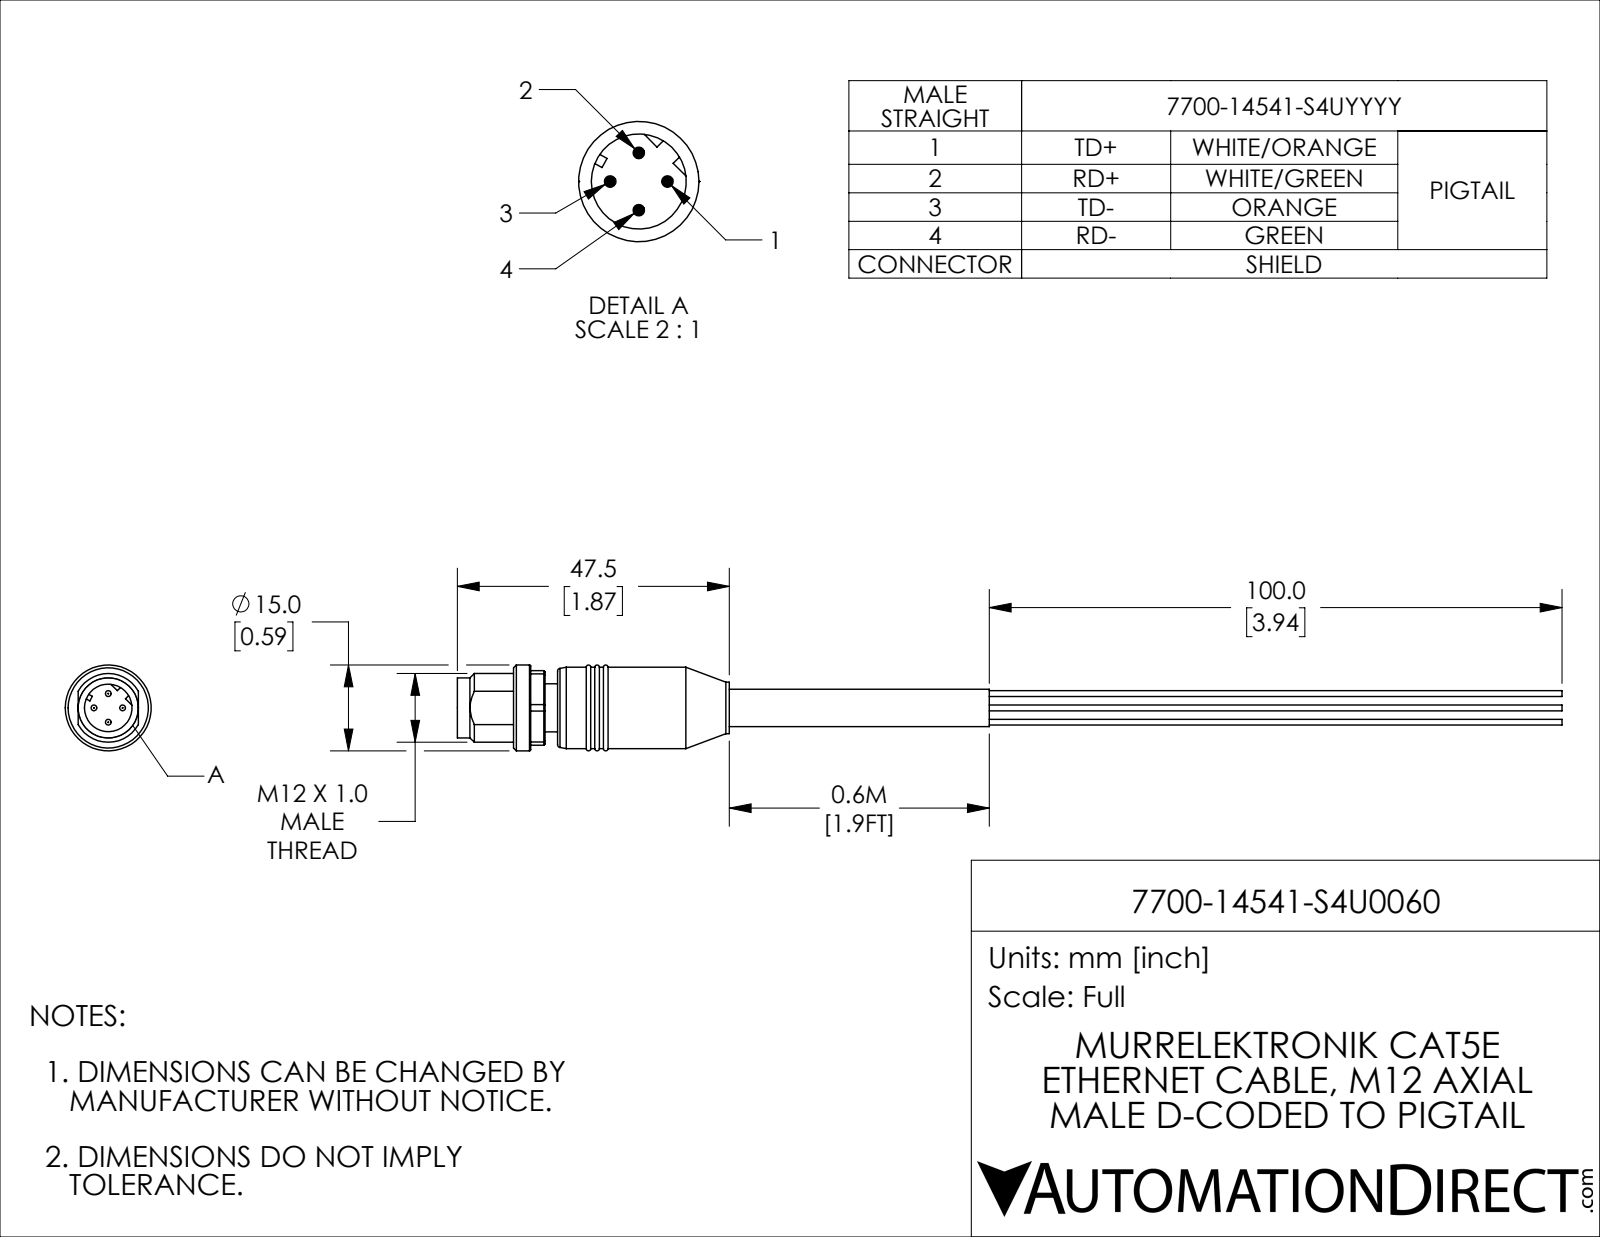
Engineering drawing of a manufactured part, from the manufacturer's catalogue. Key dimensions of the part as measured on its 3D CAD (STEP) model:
Part name (STEP PRODUCT): 7700-14541-S4U0060
STEP written by: SolidWorks 2021 (CONFIG_CONTROL_DESIGN)
Units: inches
Bodies: 1 solid, 125 faces (40 planar, 45 cylindrical, 40 other)
Overall size (bounding box): 7.594 × 0.591 × 0.591
Volume: 0.473 in³ · Surface area: 7.675 in²
Round holes (diameter × count): ⌀0.327 ×1
Round bosses / shafts (diameter × count): ⌀0.039 ×4, ⌀0.591 ×1, ⌀0.559 ×1, ⌀0.413 ×1, ⌀0.354 ×1, ⌀0.331 ×1, ⌀0.256 ×1
Partial cylindrical surfaces — rounded edges, fillets, slot ends (radius × count): R0.236 ×1, R0.283 ×1
Main face-to-face distances: 0.087, 0.035, 0.252, 0.339, 0.217, 0.303, 0.512, 0.413, 0.35, 0.386
